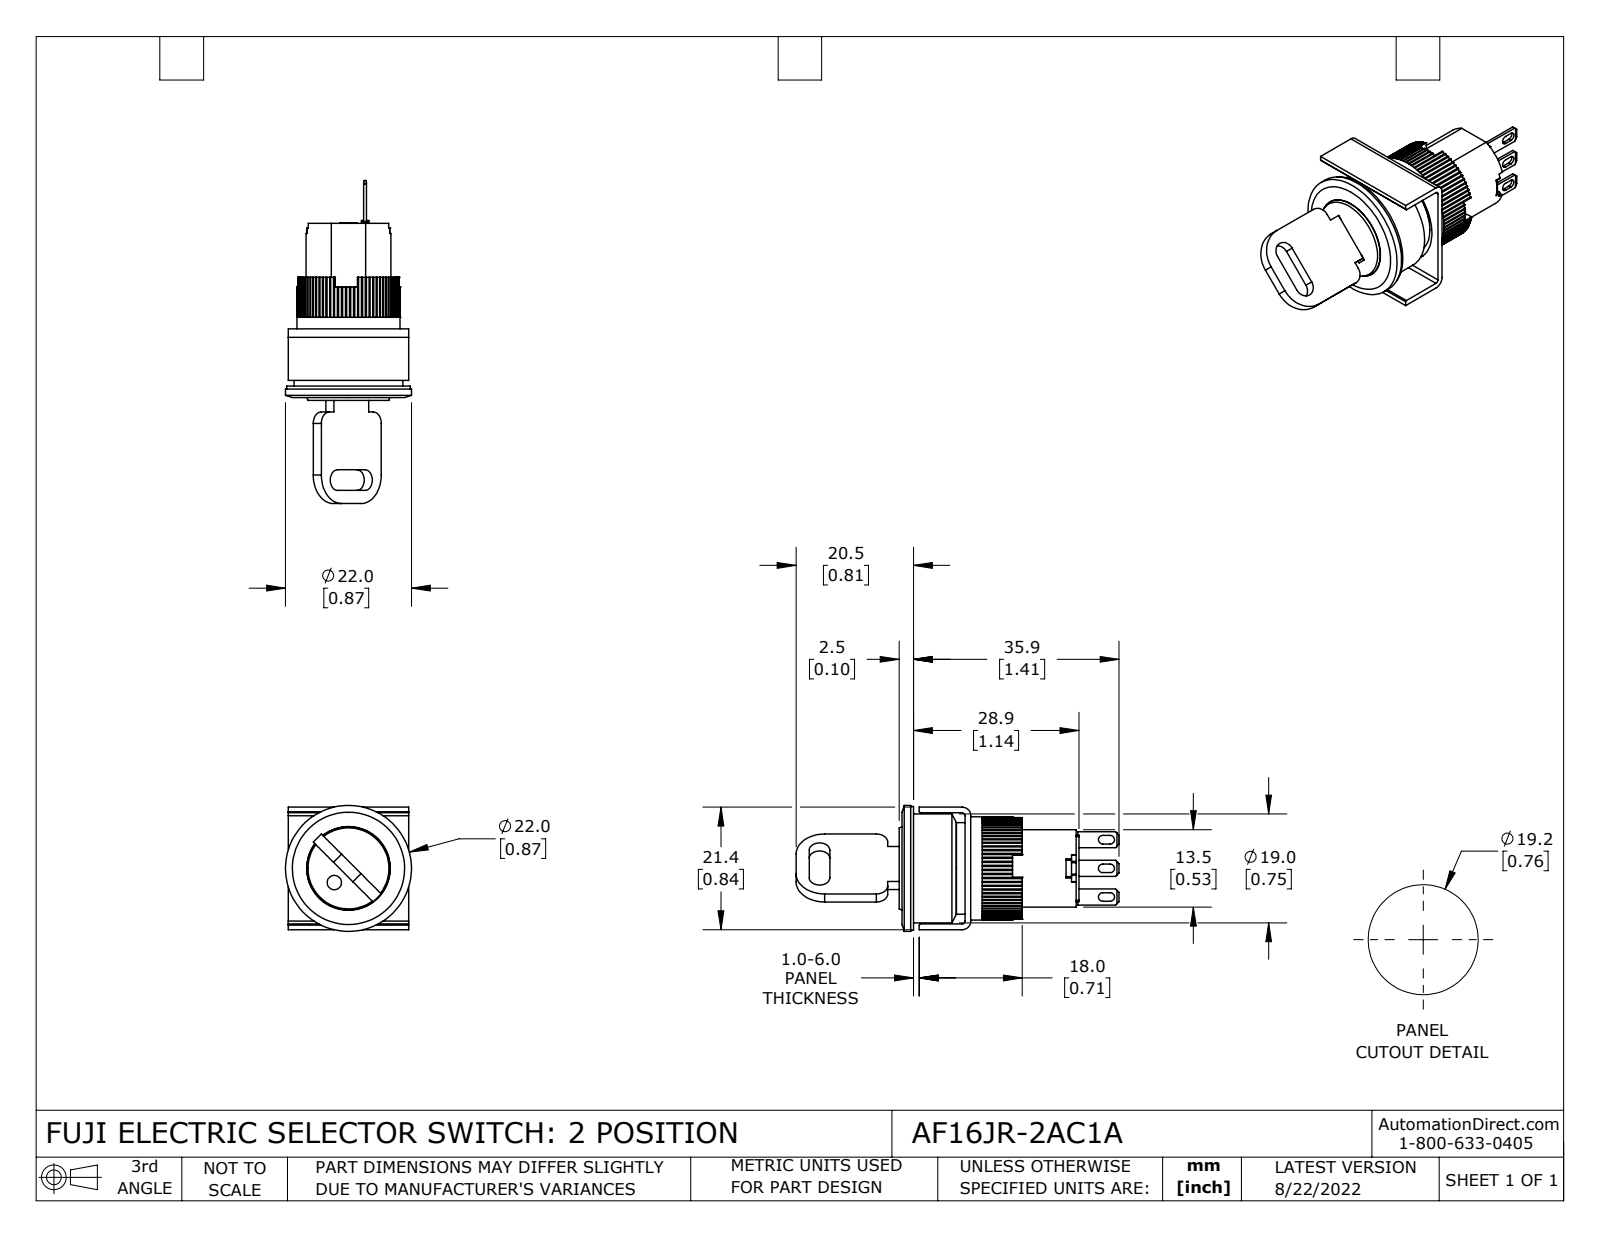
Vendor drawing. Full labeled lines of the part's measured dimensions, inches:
Part name (STEP PRODUCT): AF16JR-2AC1A
STEP written by: SolidWorks 2021 (CONFIG_CONTROL_DESIGN)
Units: inches
Bodies: 10 solids, 639 faces (456 planar, 177 cylindrical, 6 other)
Overall size (bounding box): 2.22 × 0.866 × 0.866
Volume: 0.493 in³ · Surface area: 11.01 in²
Round holes (diameter × count): ⌀0.039 ×1, ⌀0.098 ×1, ⌀0.575 ×1, ⌀0.709 ×1, ⌀0.748 ×1
Round bosses / shafts (diameter × count): ⌀0.866 ×1, ⌀0.85 ×1, ⌀0.63 ×1, ⌀0.583 ×1, ⌀0.571 ×1
Partial cylindrical surfaces — rounded edges, fillets, slot ends (radius × count): R0.01 ×80, R0.008 ×12, R0.03 ×6, R0.02 ×2, R0.059 ×2, R0.071 ×2, R0.079 ×2, R0.197 ×2
Main face-to-face distances: 0.079, 0.039, 0.02, 0.374, 0.177, 0.394, 0.803, 0.098, 0.059, 0.764
Hole centre spacings: 0.137
